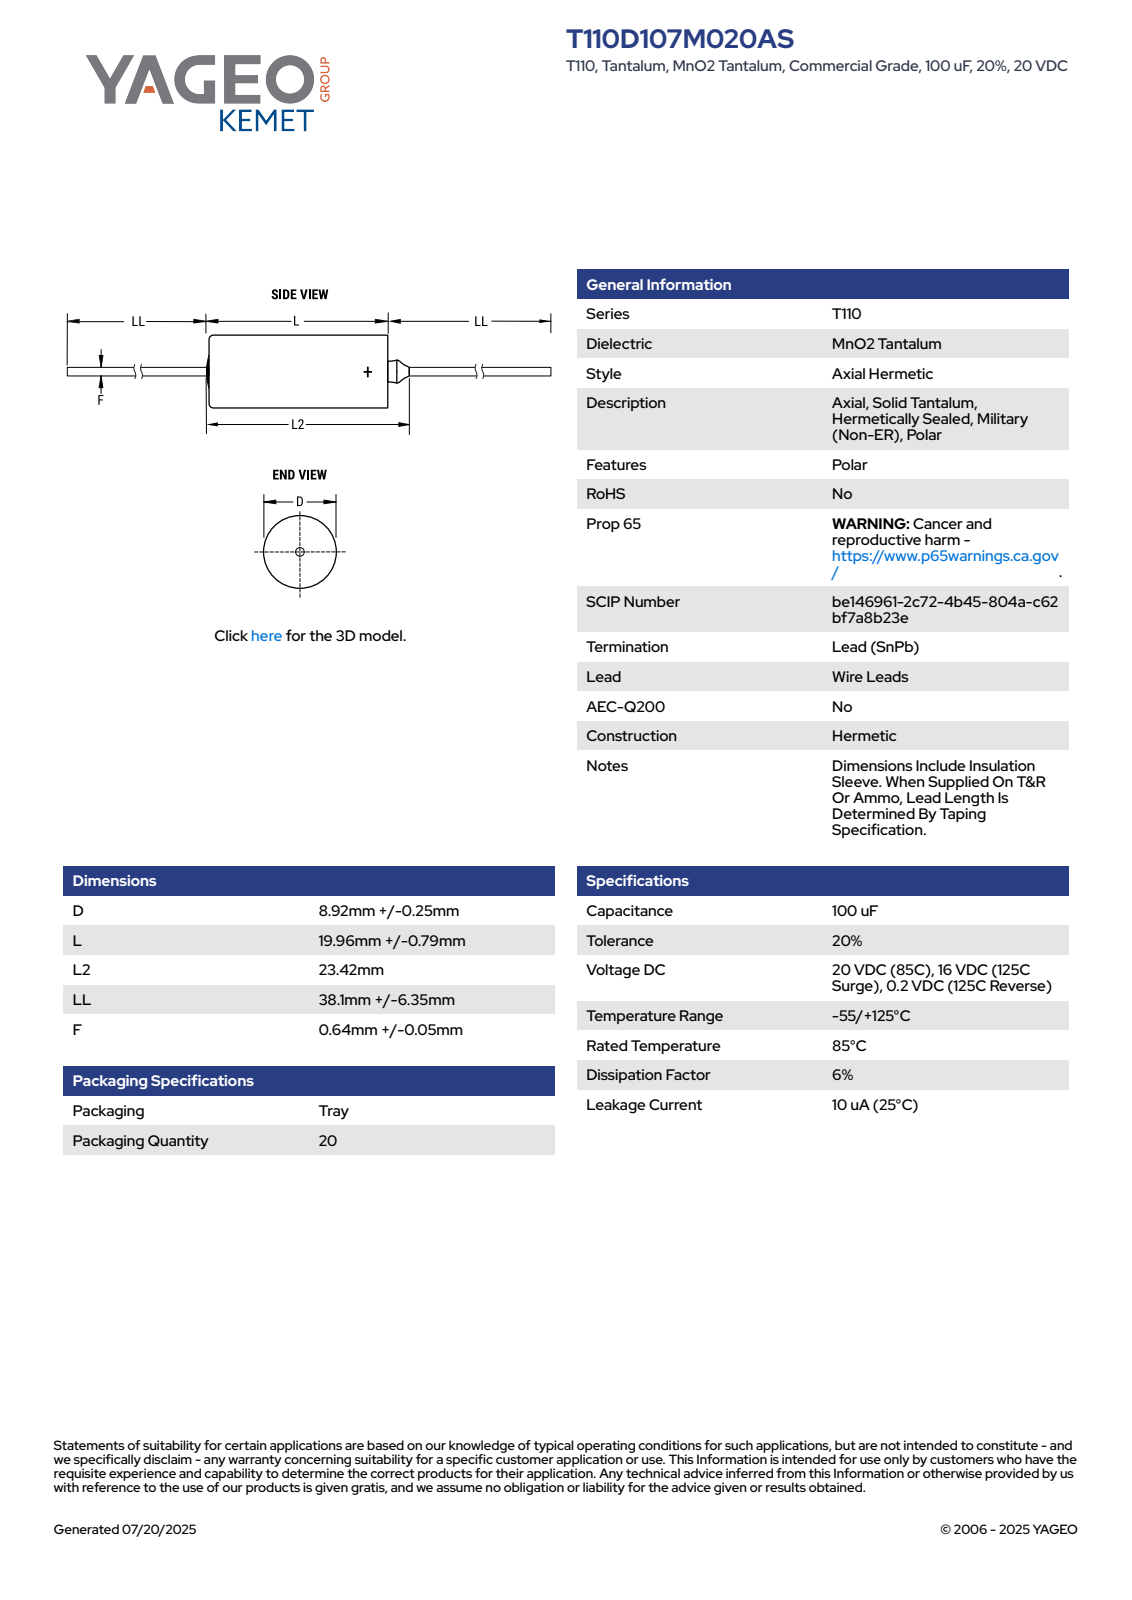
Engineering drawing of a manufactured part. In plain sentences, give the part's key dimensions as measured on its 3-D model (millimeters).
The part is named "CTAM_D_D9.17L20.75L223.42LL44.45F0.69". Its 3-D file was written by "SolidWorks 2014 (AUTOMOTIVE_DESIGN)". It is 1 solid with 98 faces: 29 planar, 30 cylindrical and 39 other. Overall it measures 109.65 by 9.17 by 9.17 millimeters. Its volume is 1 091 cubic millimeters and its surface area 1 081 square millimeters. Round holes: 1 of diameter 8.77. Round bosses or shafts: 1 of diameter 9.17, 1 of diameter 1.33, 1 of diameter 1.3, 1 of diameter 0.69. Partial cylindrical surfaces (rounded edges, fillets, slot ends): 1 of radius 4.58. The main face-to-face distances are 15.43, 20.58, 5.15, 44.62, 60.05, 65.2, 109.65, 65.03, 49.6, 44.45.
